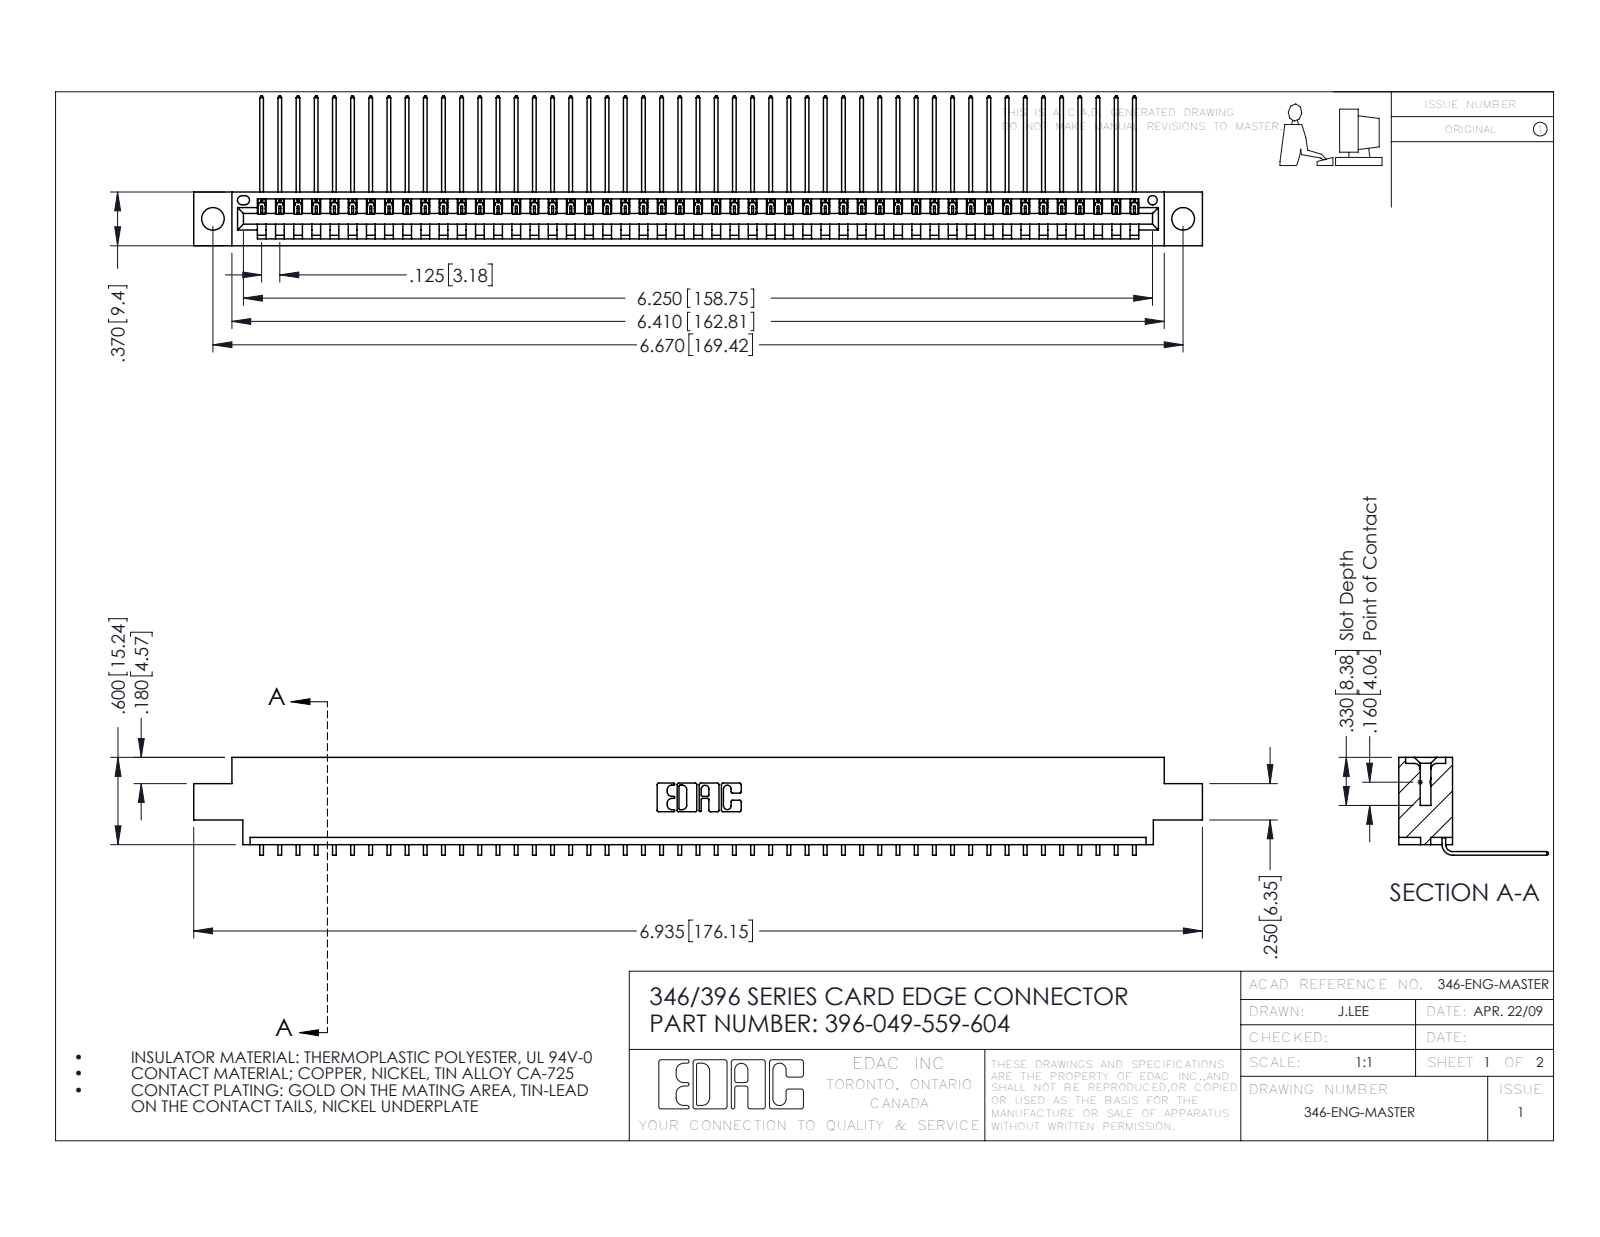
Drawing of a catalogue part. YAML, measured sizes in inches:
part_name: "345-292-001_558 559 Tail - 1; 346 Part_0.170 Offset - 0.156 Dia-TH; 396-049-559-604"
step_written_by: "SolidWorks 2016 (CONFIG_CONTROL_DESIGN)"
units: inches
bodies: {solids: 50, faces: 3066, planar: 2138, cylindrical: 928, other: 0}
overall_size: [6.935, 1.03, 0.673]
volume: 1.027
surface_area: 34.18
round_holes:
  - {diameter: 0.156, count: 2}
  - {diameter: 0.064, count: 1}
partial_cylinders:
  - {radius: 0.006, count: 98}
  - {radius: 0.01, count: 22}
  - {radius: 0.007, count: 6}
  - {radius: 0.031, count: 6}
  - {radius: 0.026, count: 3}
  - {radius: 0.031, count: 2}
  - {radius: 0.04, count: 2}
  - {radius: 0.014, count: 1}
face_to_face_distances: [0.048, 0.322, 0.37, 0.025, 0.25, 0.072, 0.298, 0.148, 0.222, 0.1]
hole_center_spacings: [0.246, 6.461, 6.67]
